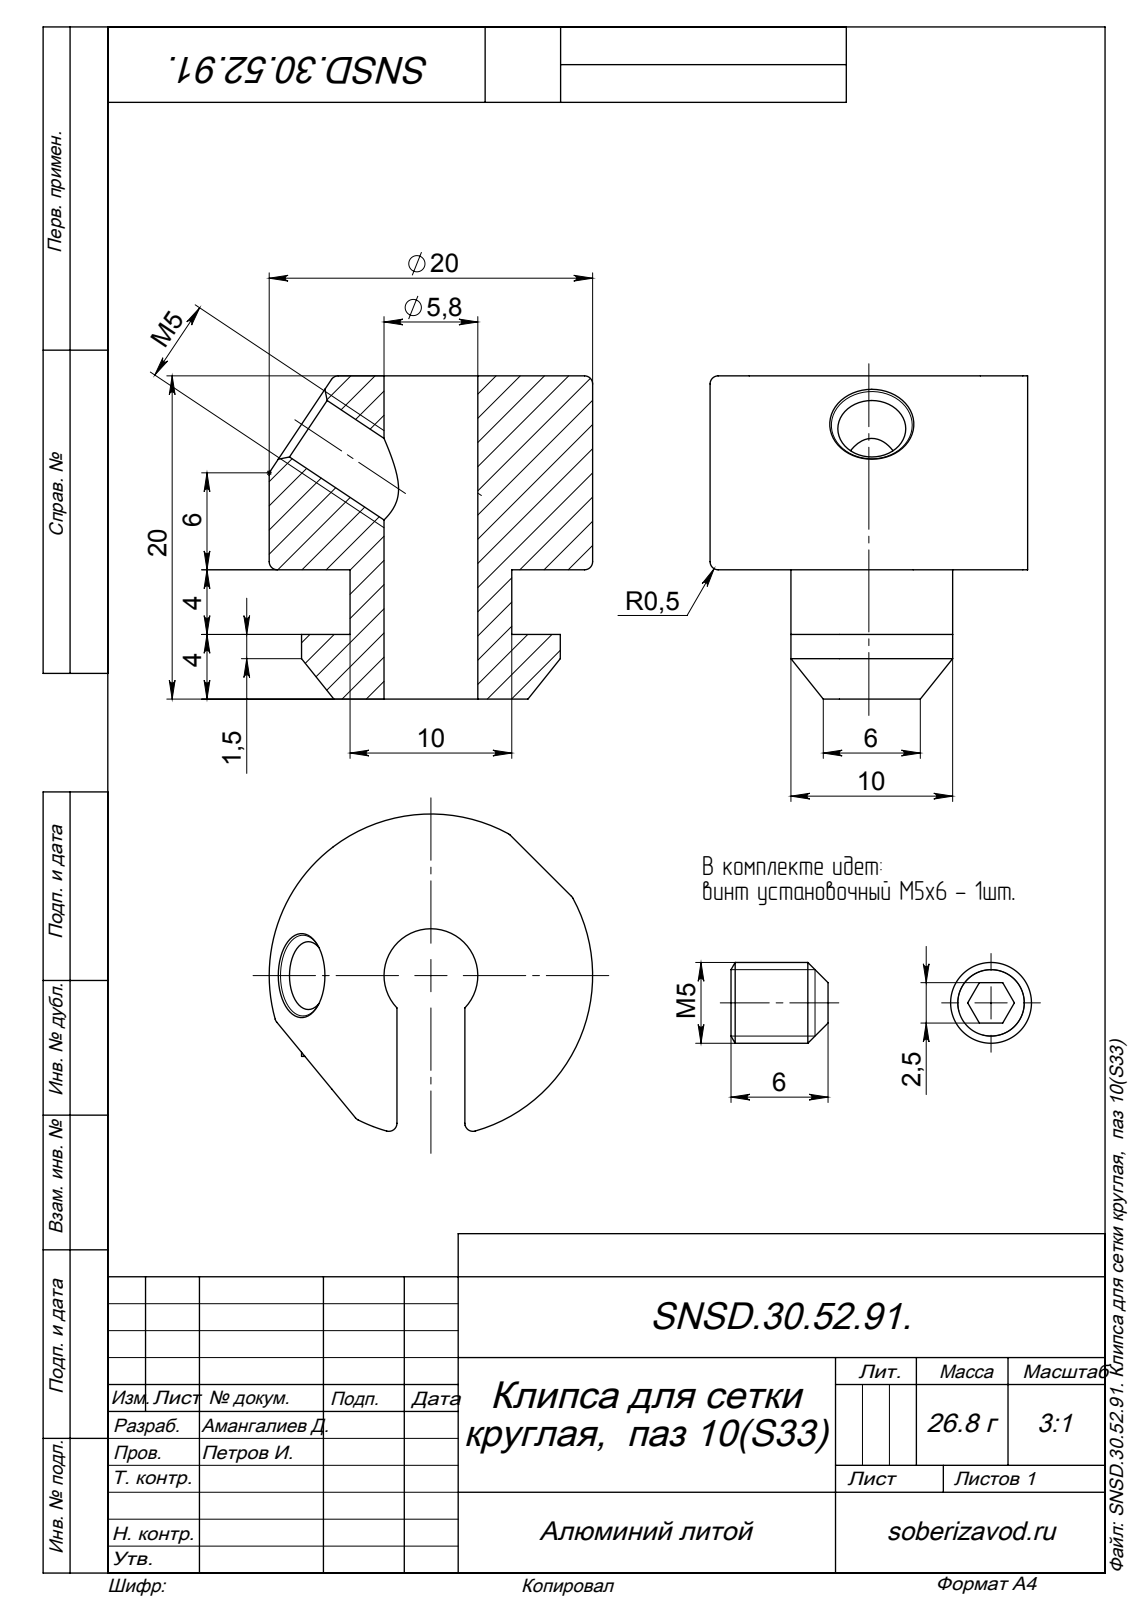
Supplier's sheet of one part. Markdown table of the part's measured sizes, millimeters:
| quantity | value |
| --- | --- |
| part name | socket set screw cup point_din; socket set screw cup point_din_DIN 916 - M5 x 6-C; SNSD.30.52.91. Клипса для сетки круглая, паз 10(S33); Установочный винт |
| STEP written by | SolidWorks 2014 (AUTOMOTIVE_DESIGN) |
| units | millimeters |
| bodies | 2 solids, 75 faces (25 planar, 25 cylindrical, 25 other) |
| overall size | 20 × 20 × 19.64 |
| volume | 3 522 mm³ |
| surface area | 2 199 mm² |
| round holes (diameter × count) | 4.2 × 1 |
| round bosses / shafts (diameter × count) | 5 × 1 |
| partial cylindrical surfaces (radius × count) | 0.5 × 12, 3 × 4, 2.9 × 1, 10 × 1 |
| main face-to-face distances | 12, 4.2, 4, 16, 2.9, 7.1, 10, 8, 20, 3 |
